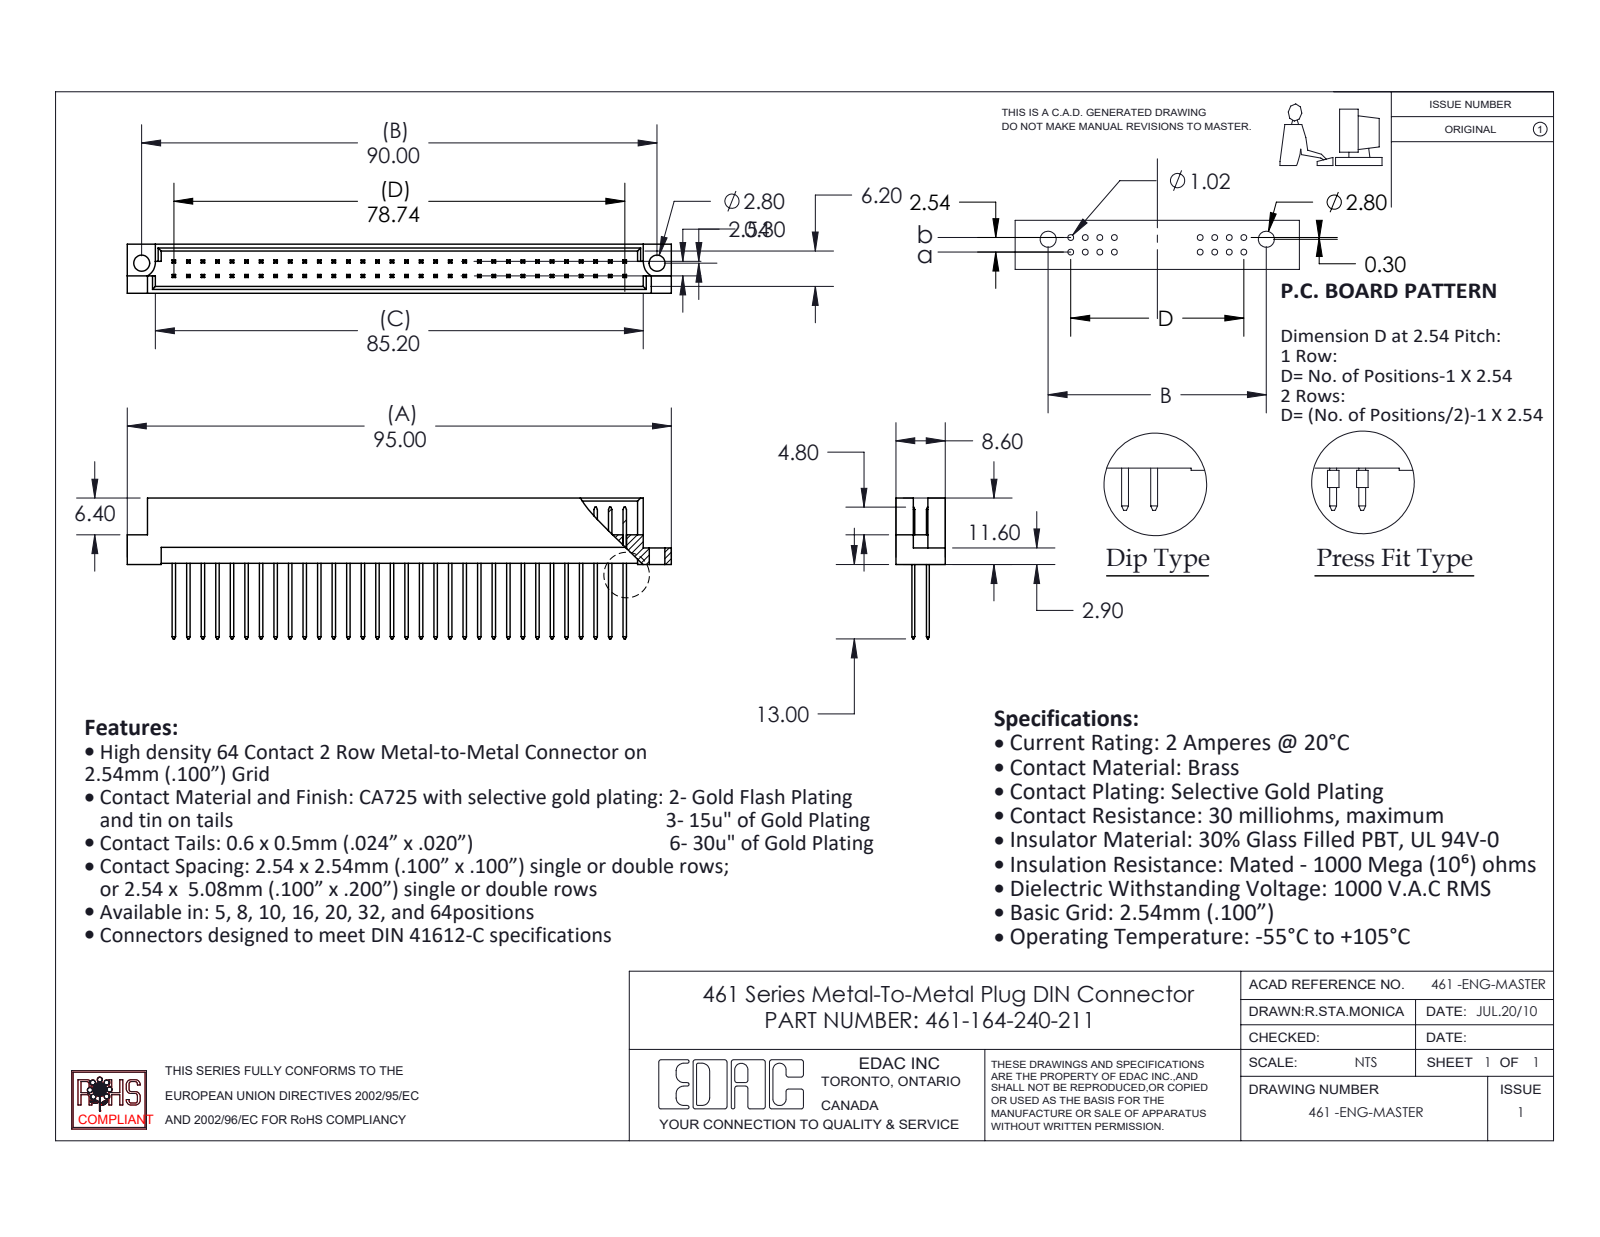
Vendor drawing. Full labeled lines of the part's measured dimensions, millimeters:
Part name (STEP PRODUCT): 461 Part_64; 461-290_40; 461-164-240-211
STEP written by: SolidWorks 2020 (CONFIG_CONTROL_DESIGN)
Units: millimetres
Bodies: 65 solids, 1201 faces (1194 planar, 7 cylindrical, 0 other)
Overall size (bounding box): 95 × 24.6 × 8.6
Volume: 5 091 mm³ · Surface area: 8 885 mm²
Round holes (diameter × count): ⌀2.8 ×2
Partial cylindrical surfaces — rounded edges, fillets, slot ends (radius × count): R2.8 ×2
Main face-to-face distances: 2.54, 1.2, 7.4, 2.78, 3.28, 5.32, 5.82, 1.58, 2.08, 4.12
Hole centre spacings: 90
